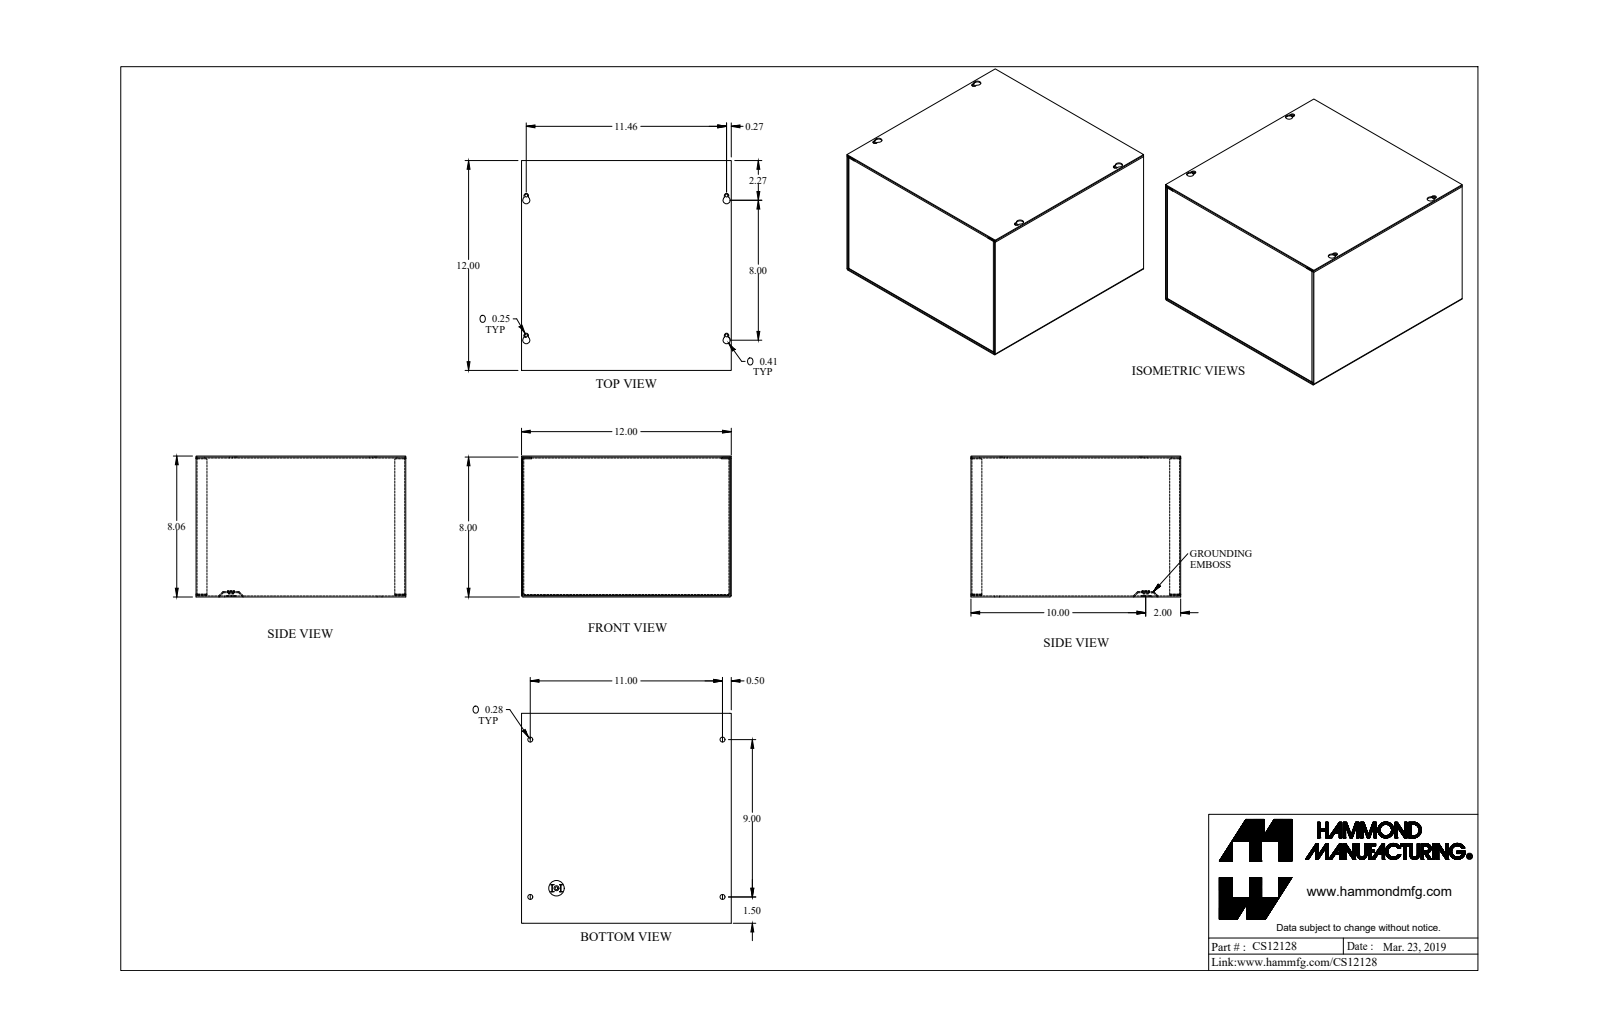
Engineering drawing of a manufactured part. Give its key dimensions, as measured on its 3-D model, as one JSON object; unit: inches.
{"part_name": "CS12128_Default", "step_written_by": "SolidWorks 2019 (CONFIG_CONTROL_DESIGN)", "units": "inches", "bodies": {"solids": 4, "faces": 205, "planar": 125, "cylindrical": 72, "other": 8}, "overall_size": [12, 12, 8.057], "volume_in3": 40.68, "surface_area_in2": 1441, "round_holes": [[0.17, 5], [0.281, 4], [0.5, 1]], "round_bosses_or_shafts": [[0.492, 1], [0.284, 1]], "partial_cylinders_radius": [[0.029, 12], [0.086, 12], [0.057, 8], [0.125, 4], [0.203, 4]], "face_to_face_distances": [0.057, 11.943, 8, 12, 11.886, 7.943, 8.057, 0.07, 11.873, 0.08], "hole_center_spacings": [0.55, 8.503, 11.241, 14.084, 8, 9, 11, 11.46]}
